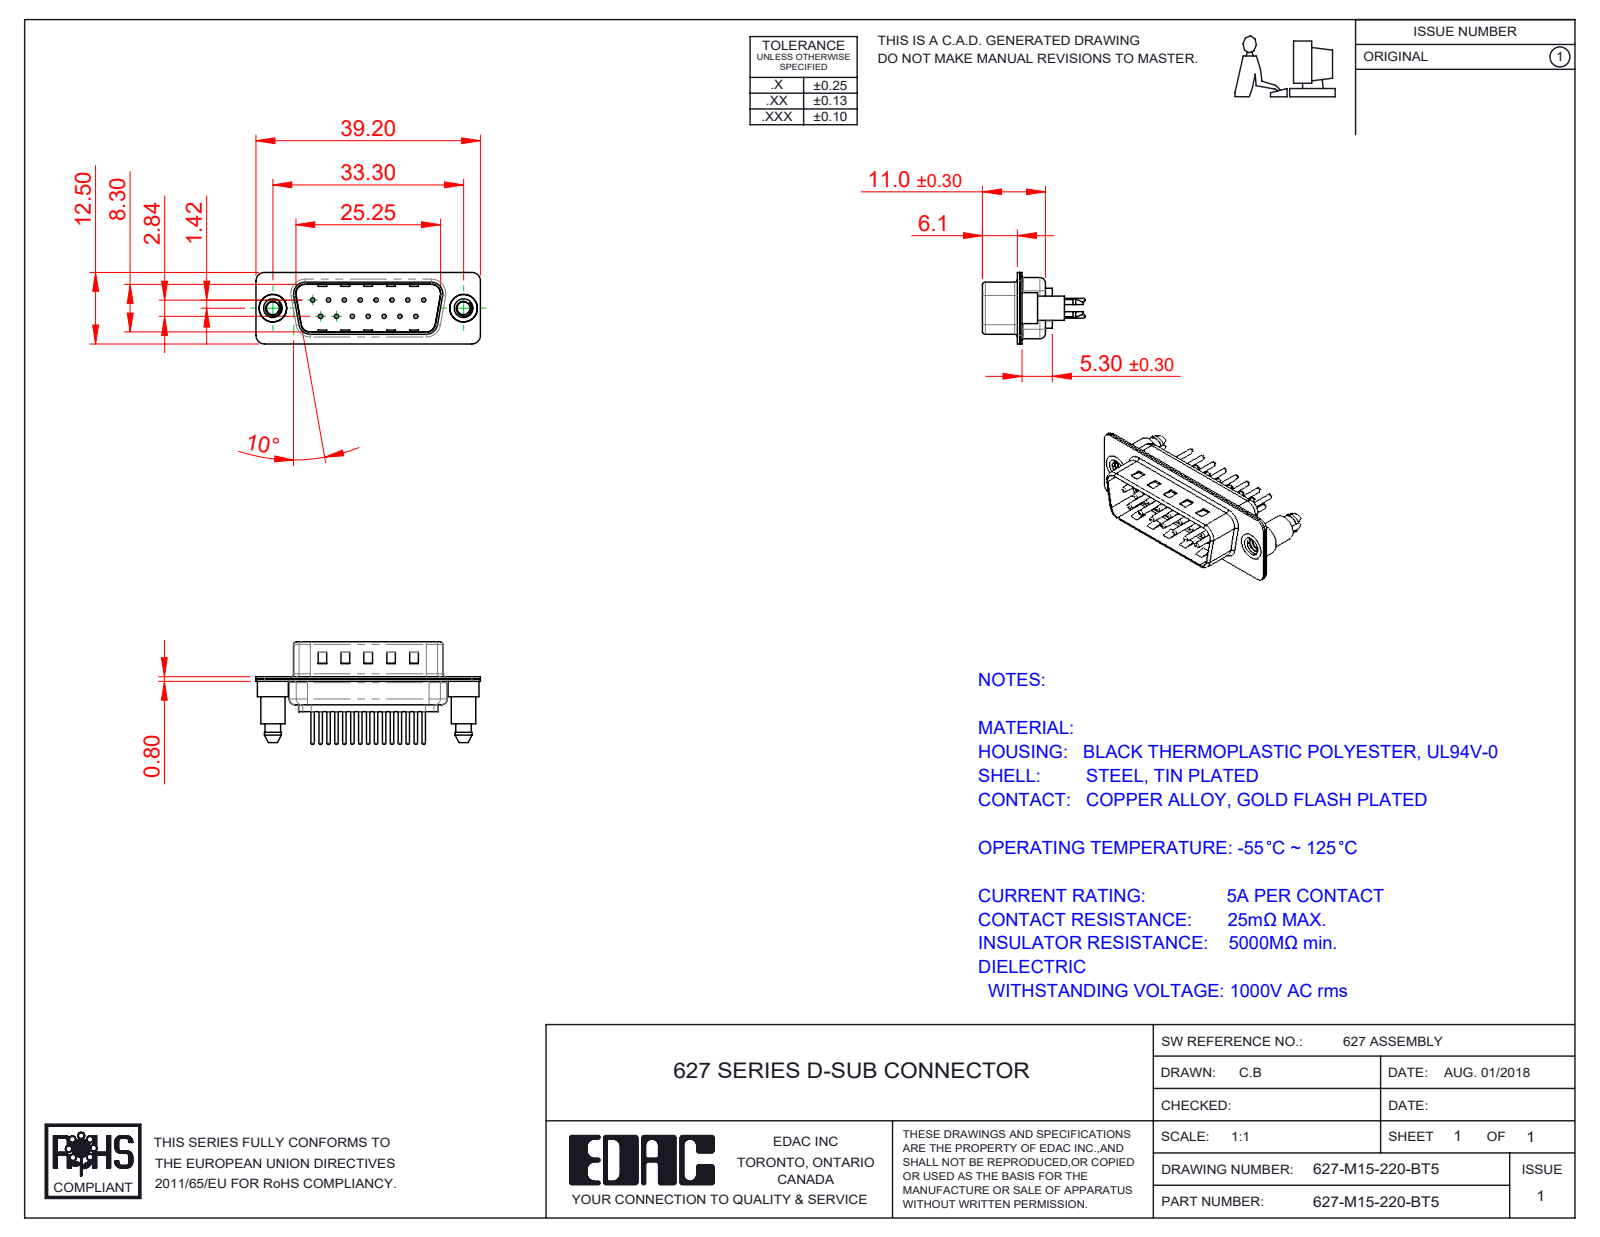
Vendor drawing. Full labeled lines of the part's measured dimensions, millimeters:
Part name (STEP PRODUCT): 627M Housing_15 Contacts; 627M Shell Front_15 Contacts; 627M Contact Row 2_20; 627M Shell Rear_15 Contacts (+3 more)
STEP written by: SolidWorks 2020 (CONFIG_CONTROL_DESIGN)
Units: millimetres
Bodies: 20 solids, 945 faces (260 planar, 375 cylindrical, 310 other)
Overall size (bounding box): 39.2 × 17.9 × 12.5
Volume: 1 977 mm³ · Surface area: 5 141 mm²
Round holes (diameter × count): ⌀0.75 ×15, ⌀1.6 ×15, ⌀2 ×15, ⌀2.26 ×2, ⌀4 ×2, ⌀4.8 ×2
Round bosses / shafts (diameter × count): ⌀1.5 ×15, ⌀0.6 ×15, ⌀5.4 ×2, ⌀4.9 ×2, ⌀4.25 ×2
Partial cylindrical surfaces — rounded edges, fillets, slot ends (radius × count): R1.5 ×18, R2 ×12, R1.6 ×10, R0.5 ×8, R0.25 ×4, R0.6 ×4, R0.65 ×4, R0.9 ×4
Main face-to-face distances: 0.4, 0.8, 9.5, 9.1, 8.7, 9.9, 5.3, 1.2, 6.1, 5.7
Hole centre spacings: 3.16, 2.77, 5.54, 8.31, 11.08, 5.03, 5.04, 7.48
